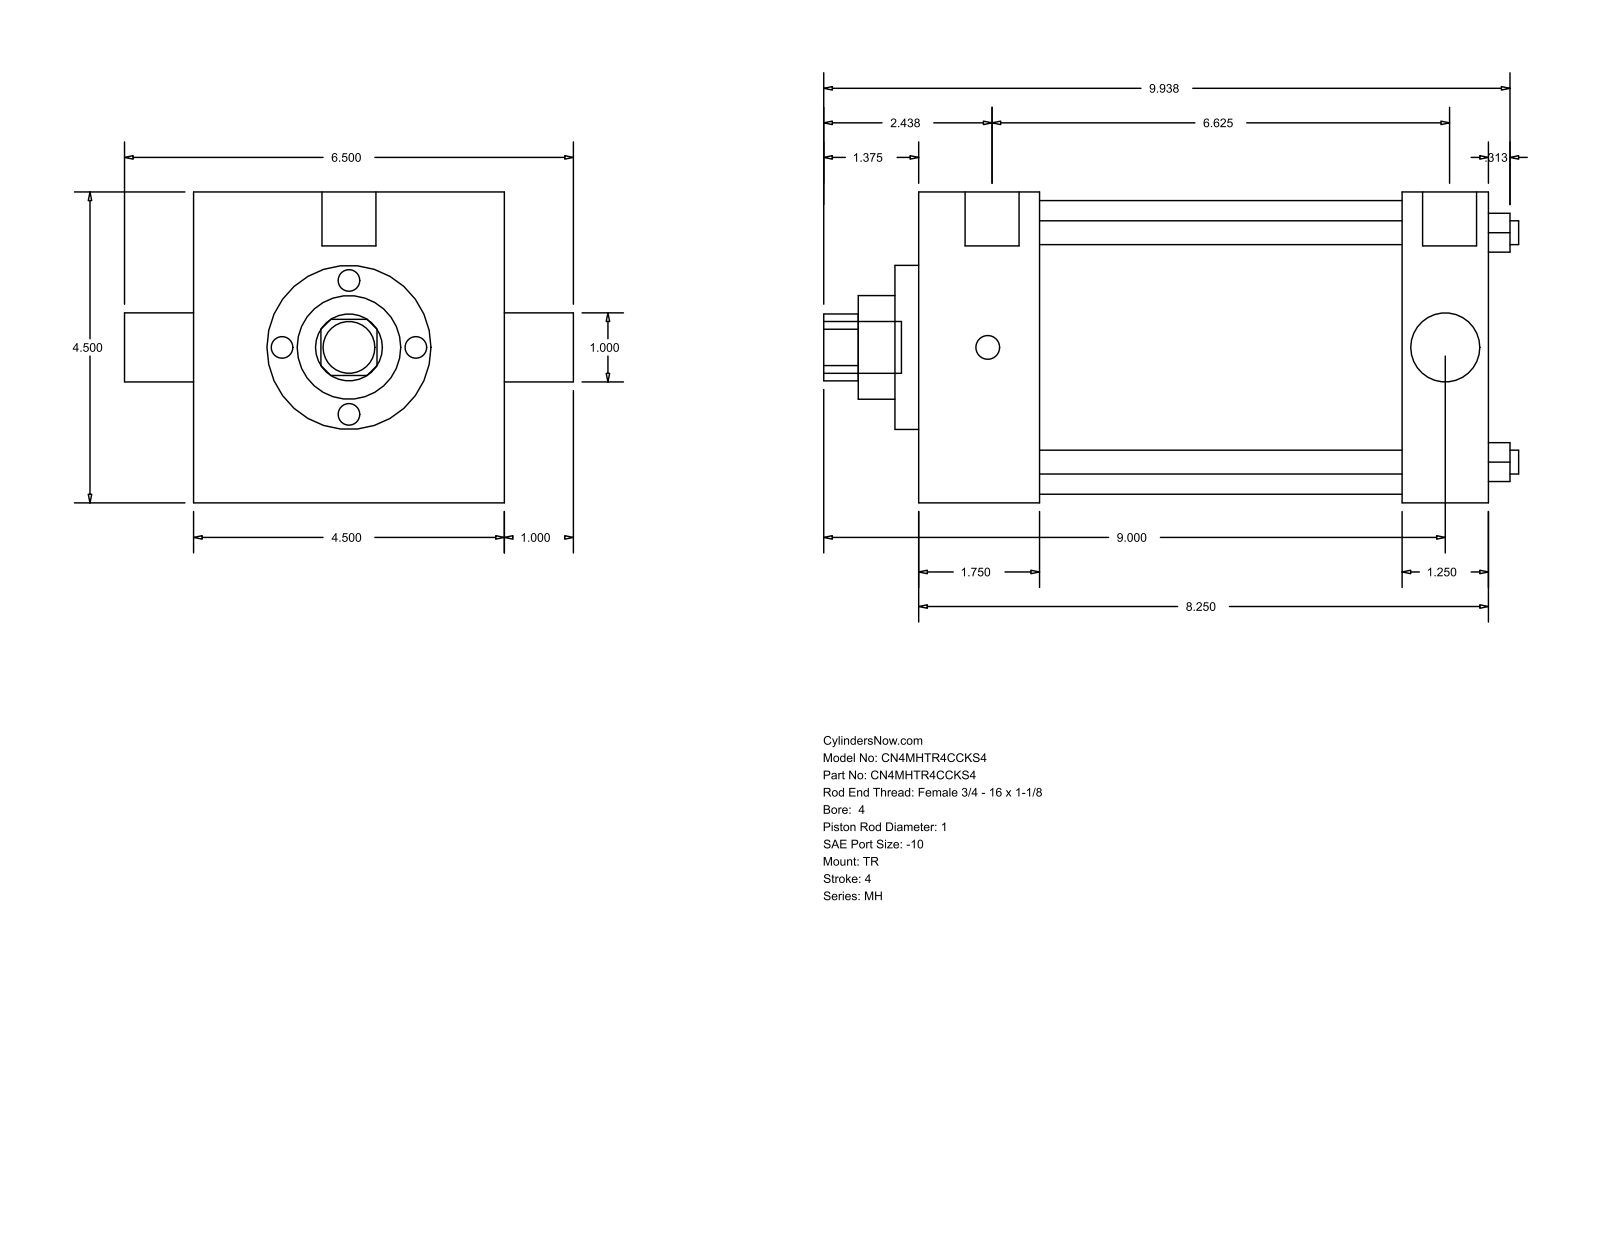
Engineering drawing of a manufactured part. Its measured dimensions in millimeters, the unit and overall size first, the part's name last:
Units: millimetres
Overall size (bounding box): 255.59 × 165.1 × 114.3
Round holes (diameter × count): ⌀8.76 ×4, ⌀25.4 ×2, ⌀38.1 ×1, ⌀60.33 ×1, ⌀107.95 ×1
Round bosses / shafts (diameter × count): ⌀8.73 ×3, ⌀19.84 ×2, ⌀19.05 ×1
Partial cylindrical surfaces — rounded edges, fillets, slot ends (radius × count): R12.29 ×1
Main face-to-face distances: 114.3, 209.55, 44.46, 165.09, 177.8, 133.34, 31.75, 8.73, 53.19, 186.53
Hole centre spacings: 59.62, 84.32, 119.25
Bodies: 0 solids, 86 faces (61 planar, 25 cylindrical, 0 other)
Part name (STEP PRODUCT): MH_TR__0400_1
STEP written by: GSSL Pune (CONFIG_CONTROL_DESIGN)
